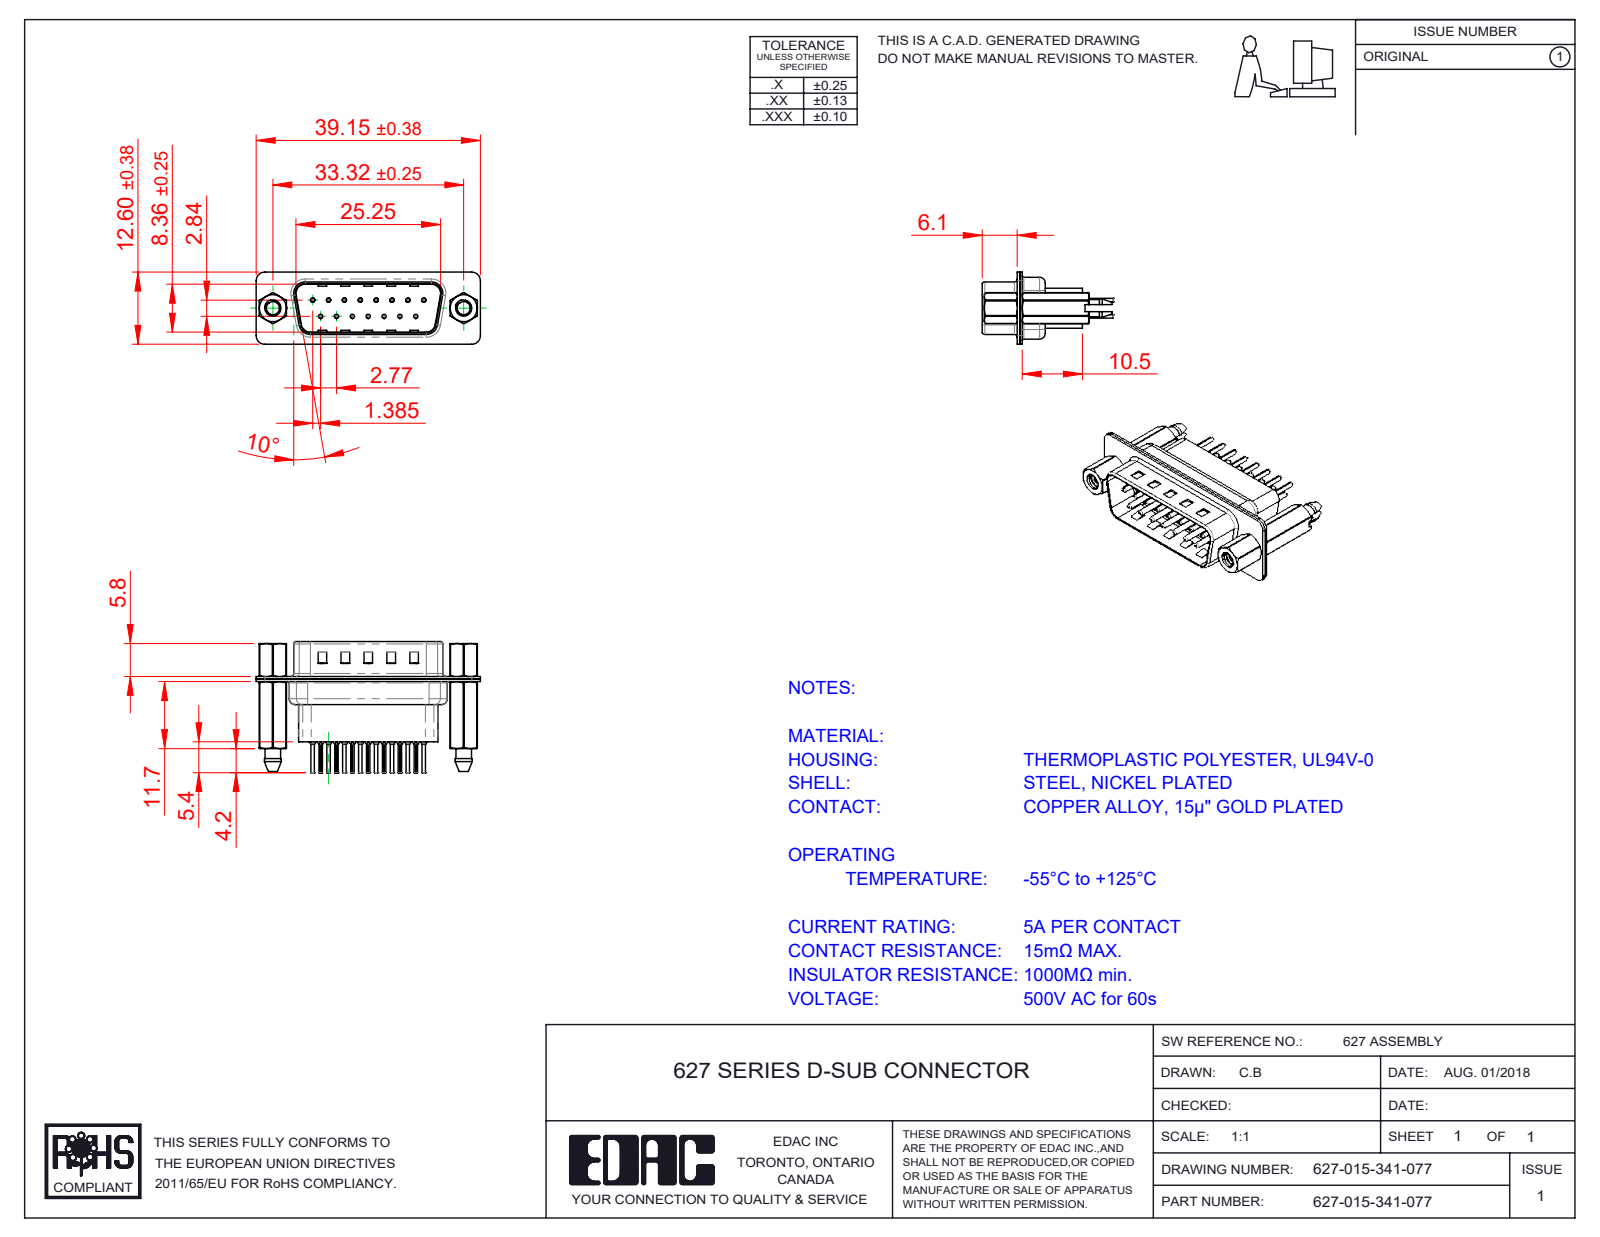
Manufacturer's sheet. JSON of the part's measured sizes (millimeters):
{"part_name": "627 Contact Row 1_41; 627 Housing_15 HP; 627 4-40 Threaded Boardlock_HP41; 627 Contact Row 2_41 (+4 more)", "step_written_by": "SolidWorks 2020 (CONFIG_CONTROL_DESIGN)", "units": "millimeters", "bodies": {"solids": 22, "faces": 2044, "planar": 553, "cylindrical": 826, "other": 665}, "overall_size": [39.15, 22.8, 12.6], "volume_mm3": 3039, "surface_area_mm2": 7805, "round_holes": [[0.2, 15], [0.35, 15], [1.1, 15], [1.6, 15], [2.26, 2], [2.29, 2], [4, 2], [4.8, 2]], "round_bosses_or_shafts": [[2, 15], [1.5, 15], [0.75, 15], [0.6, 15], [4.9, 2], [2.79, 2]], "partial_cylinders_radius": [[0.1, 30], [1.5, 18], [2, 12], [1.6, 10], [0.5, 8], [0.25, 4], [0.6, 4], [0.65, 4]], "face_to_face_distances": [0.4, 0.45, 0.9, 4.76, 0.82, 9.58, 1.5, 0.68, 7.68, 1.4], "hole_center_spacings": [3.16, 2.77, 5.54, 8.31, 11.08, 5.03, 5.04, 7.48]}
